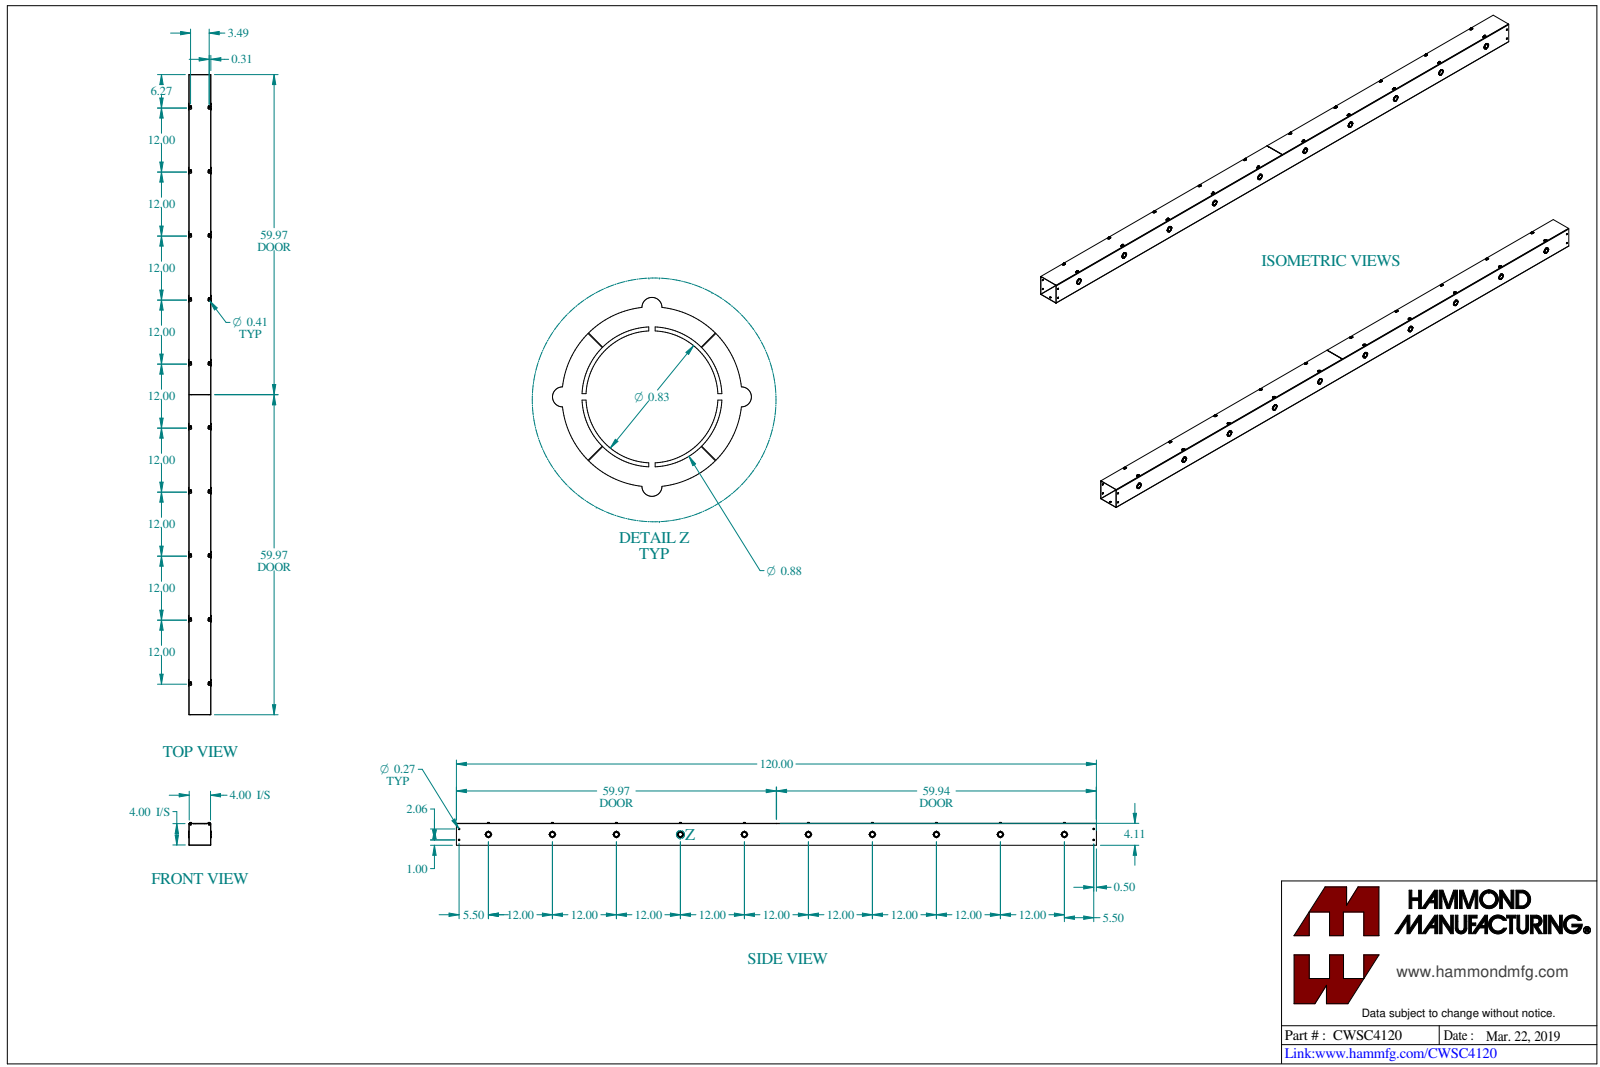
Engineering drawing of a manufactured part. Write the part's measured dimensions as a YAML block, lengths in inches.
part_name: "CWSC4120"
step_written_by: "SolidWorks 2023 (CONFIG_CONTROL_DESIGN)"
units: inches
bodies: {solids: 23, faces: 1522, planar: 674, cylindrical: 728, other: 120}
overall_size: [120, 4.289, 4.258]
volume: 117.5
surface_area: 4115
round_holes:
  - {diameter: 0.177, count: 20}
  - {diameter: 0.875, count: 10}
  - {diameter: 0.266, count: 4}
  - {diameter: 0.313, count: 2}
round_bosses_or_shafts:
  - {diameter: 0.375, count: 20}
  - {diameter: 0.19, count: 20}
  - {diameter: 1.125, count: 10}
  - {diameter: 1.125, count: 10}
  - {diameter: 0.825, count: 10}
partial_cylinders:
  - {radius: 0.062, count: 30}
  - {radius: 0.125, count: 20}
  - {radius: 0.203, count: 20}
  - {radius: 0.063, count: 10}
  - {radius: 0.029, count: 4}
  - {radius: 0.086, count: 4}
face_to_face_distances: [0.057, 4.057, 4, 4.114, 3.943, 0.114, 0.072, 0.129, 4.129, 4.186]
hole_center_spacings: [12, 24, 36, 12.497, 48, 24.252, 60, 36.169]
